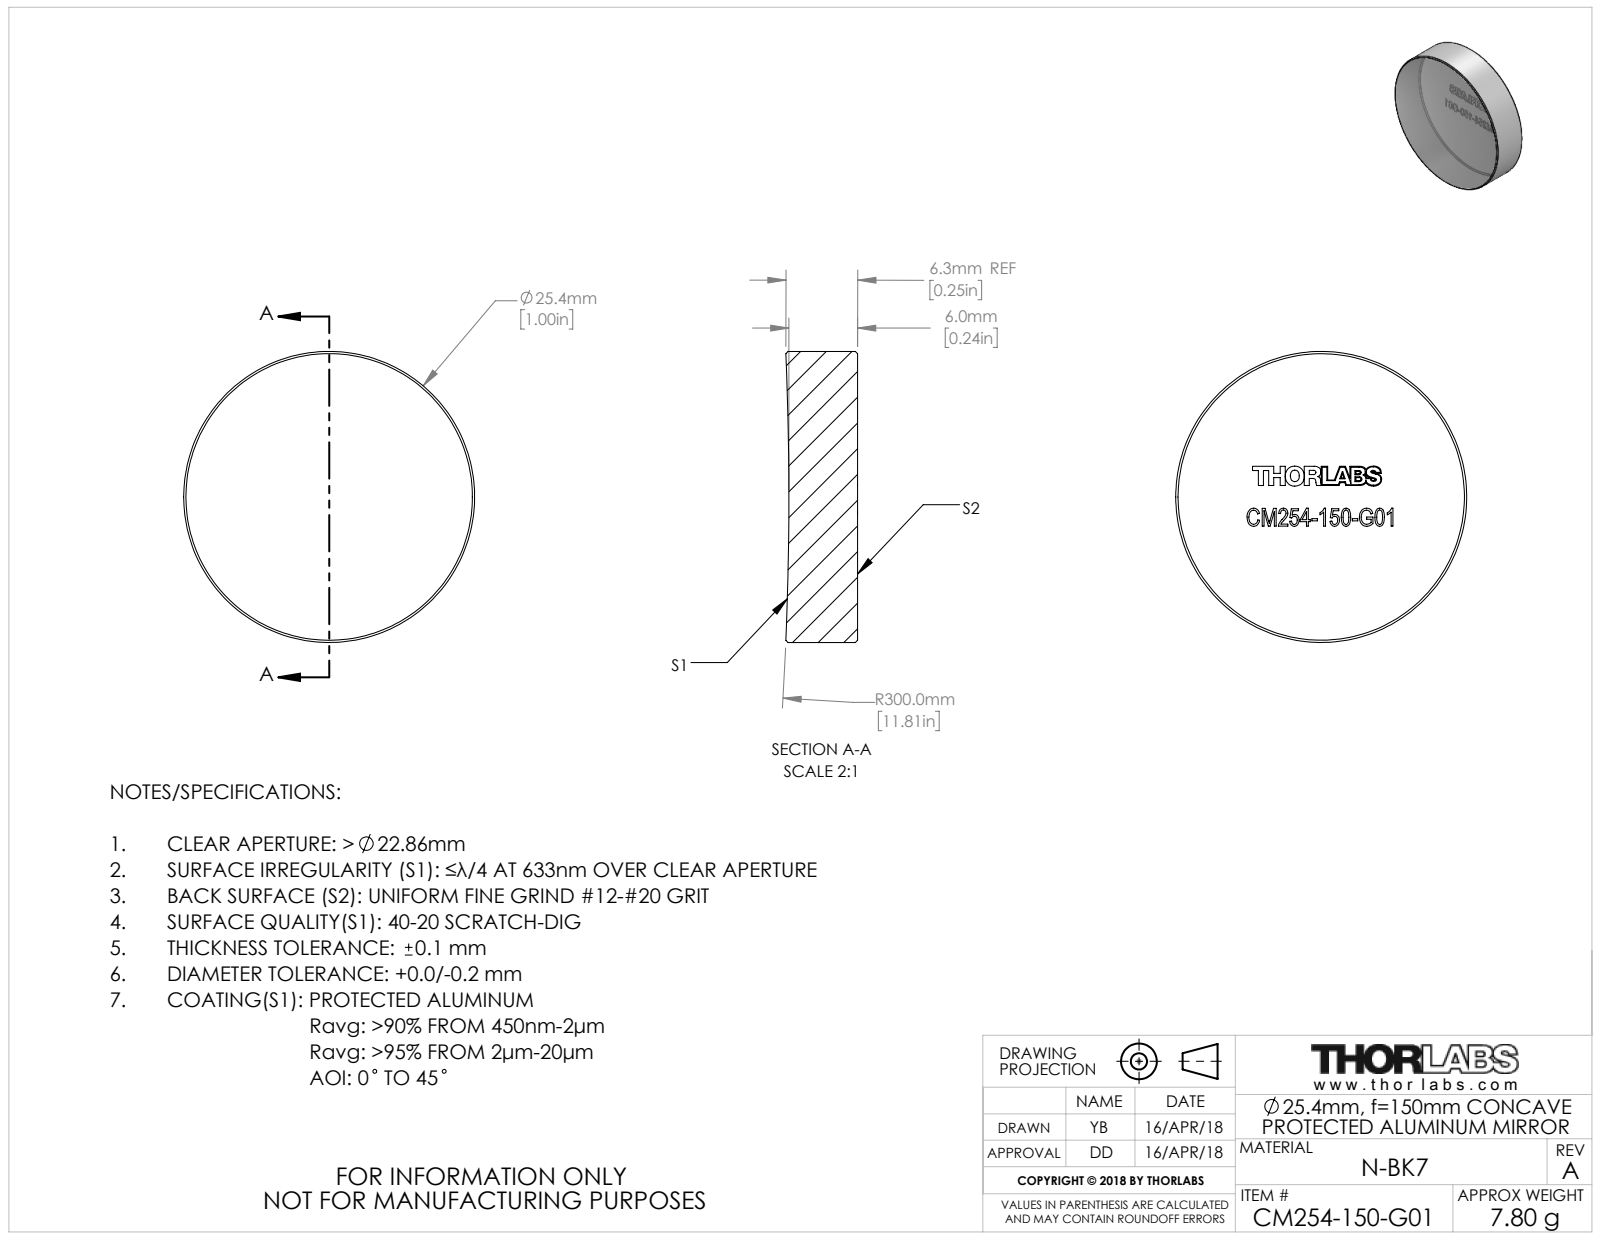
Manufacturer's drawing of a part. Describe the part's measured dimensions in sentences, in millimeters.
The part is named "TTN153272-E0W". Its 3-D file was written by "SolidWorks 2018 (CONFIG_CONTROL_DESIGN)". It is 1 solid with 40 faces: 32 planar, 2 cylindrical and 6 other. Overall it measures 25.4 by 25.4 by 6.26 millimeters. Its volume is 3 105 cubic millimeters and its surface area 1 495 square millimeters. Round bosses or shafts: 1 of diameter 25.4.
